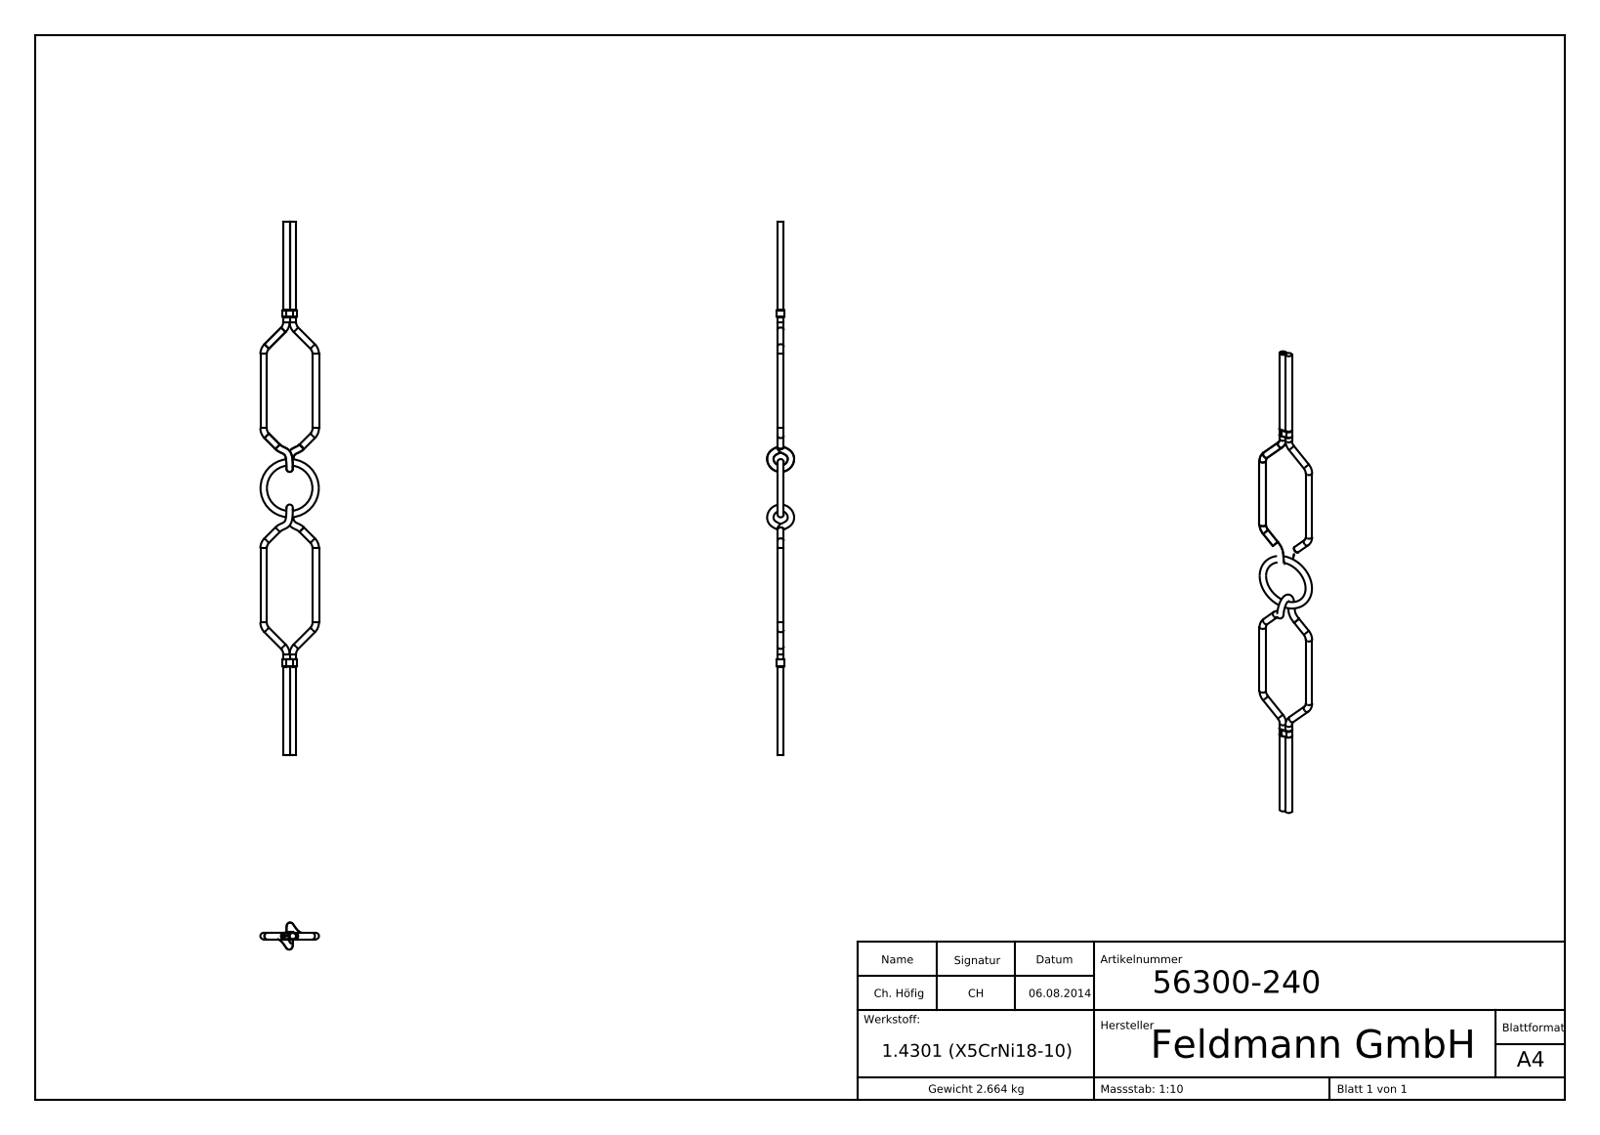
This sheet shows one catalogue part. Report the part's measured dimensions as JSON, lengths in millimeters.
{"part_name": "56300-240", "step_written_by": "SolidWorks 2015 (CONFIG_CONTROL_DESIGN)", "units": "millimeters", "bodies": {"solids": 6, "faces": 352, "planar": 148, "cylindrical": 56, "other": 148}, "overall_size": [1000, 110, 50.64], "volume_mm3": 337208, "surface_area_mm2": 115627, "round_bosses_or_shafts": [[12, 12]], "partial_cylinders_radius": [[1, 8], [7, 2], [6.03, 1]], "face_to_face_distances": [14, 1000, 999.5, 0.5, 0.39, 2.97, 1.12, 7, 4.09, 0.73]}
